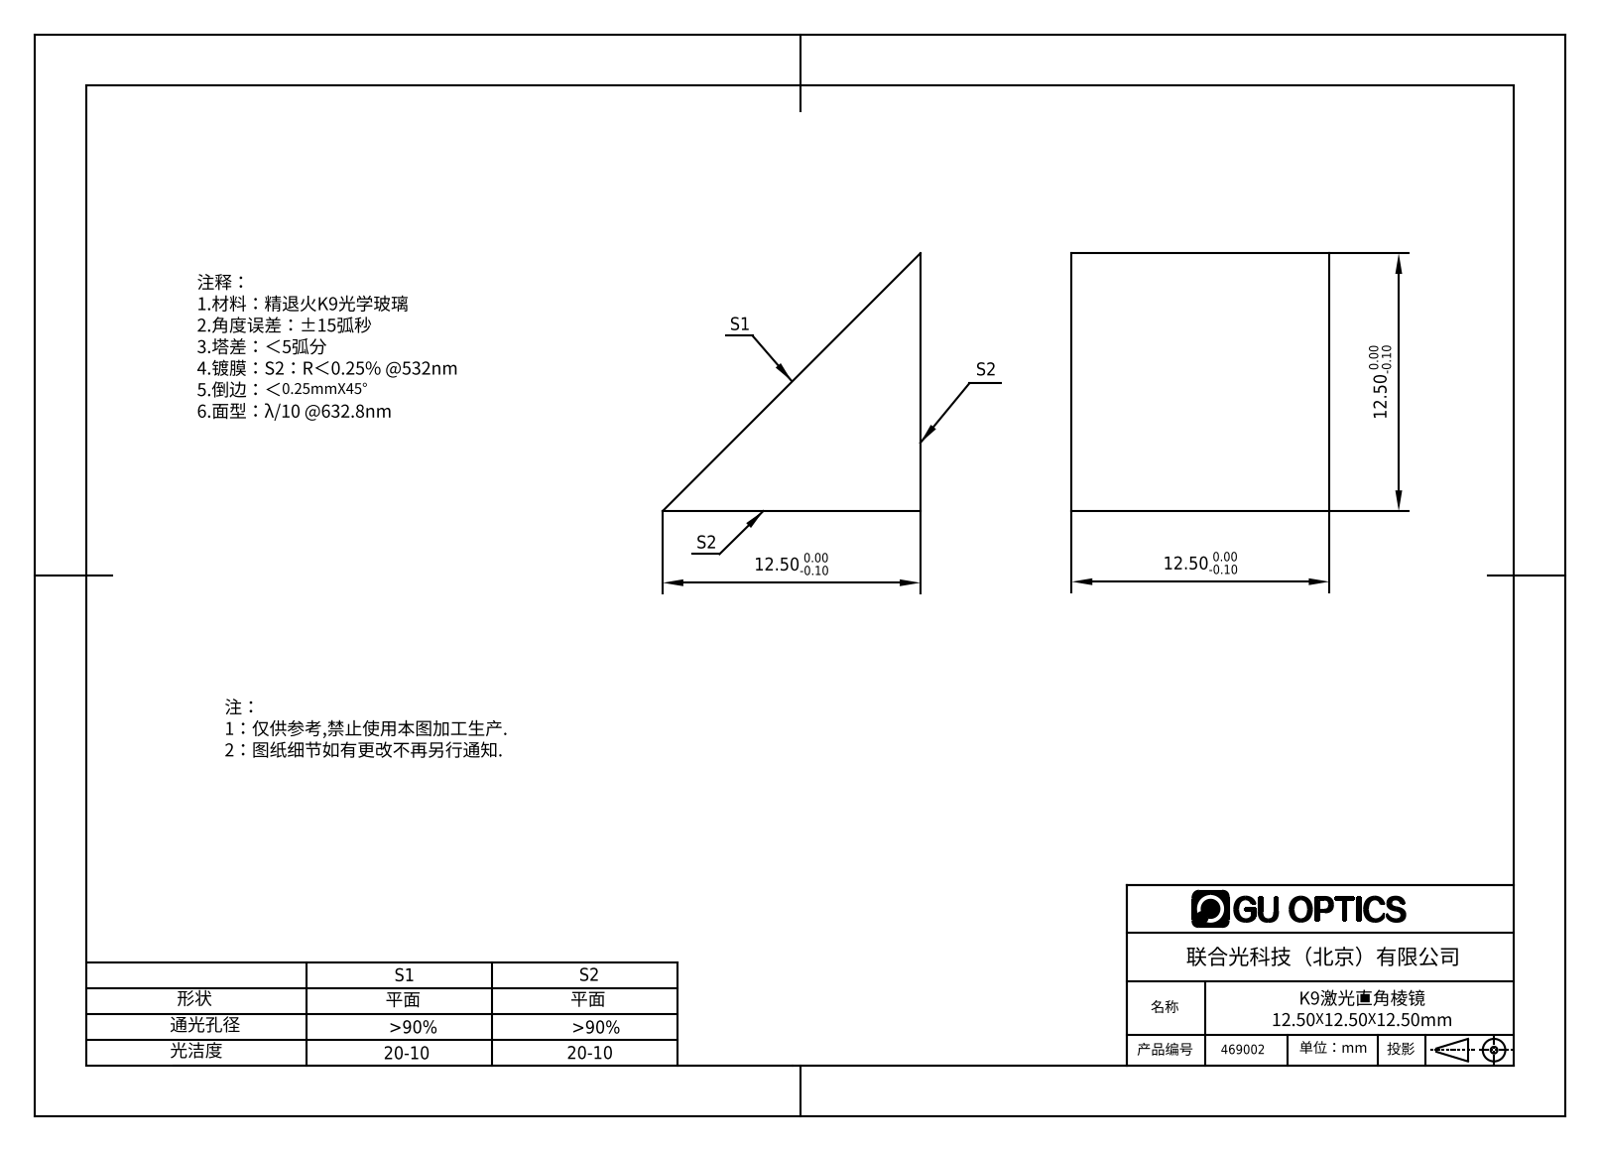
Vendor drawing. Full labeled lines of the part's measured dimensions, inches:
Part name (STEP PRODUCT): 469002
STEP written by: SolidWorks 2016 (AUTOMOTIVE_DESIGN)
Units: inches
Bodies: 1 solid, 5 faces (5 planar, 0 cylindrical, 0 other)
Overall size (bounding box): 0.617 × 0.492 × 0.411
Volume: 0.058 in³ · Surface area: 1.03 in²
Main face-to-face distances: 0.492
